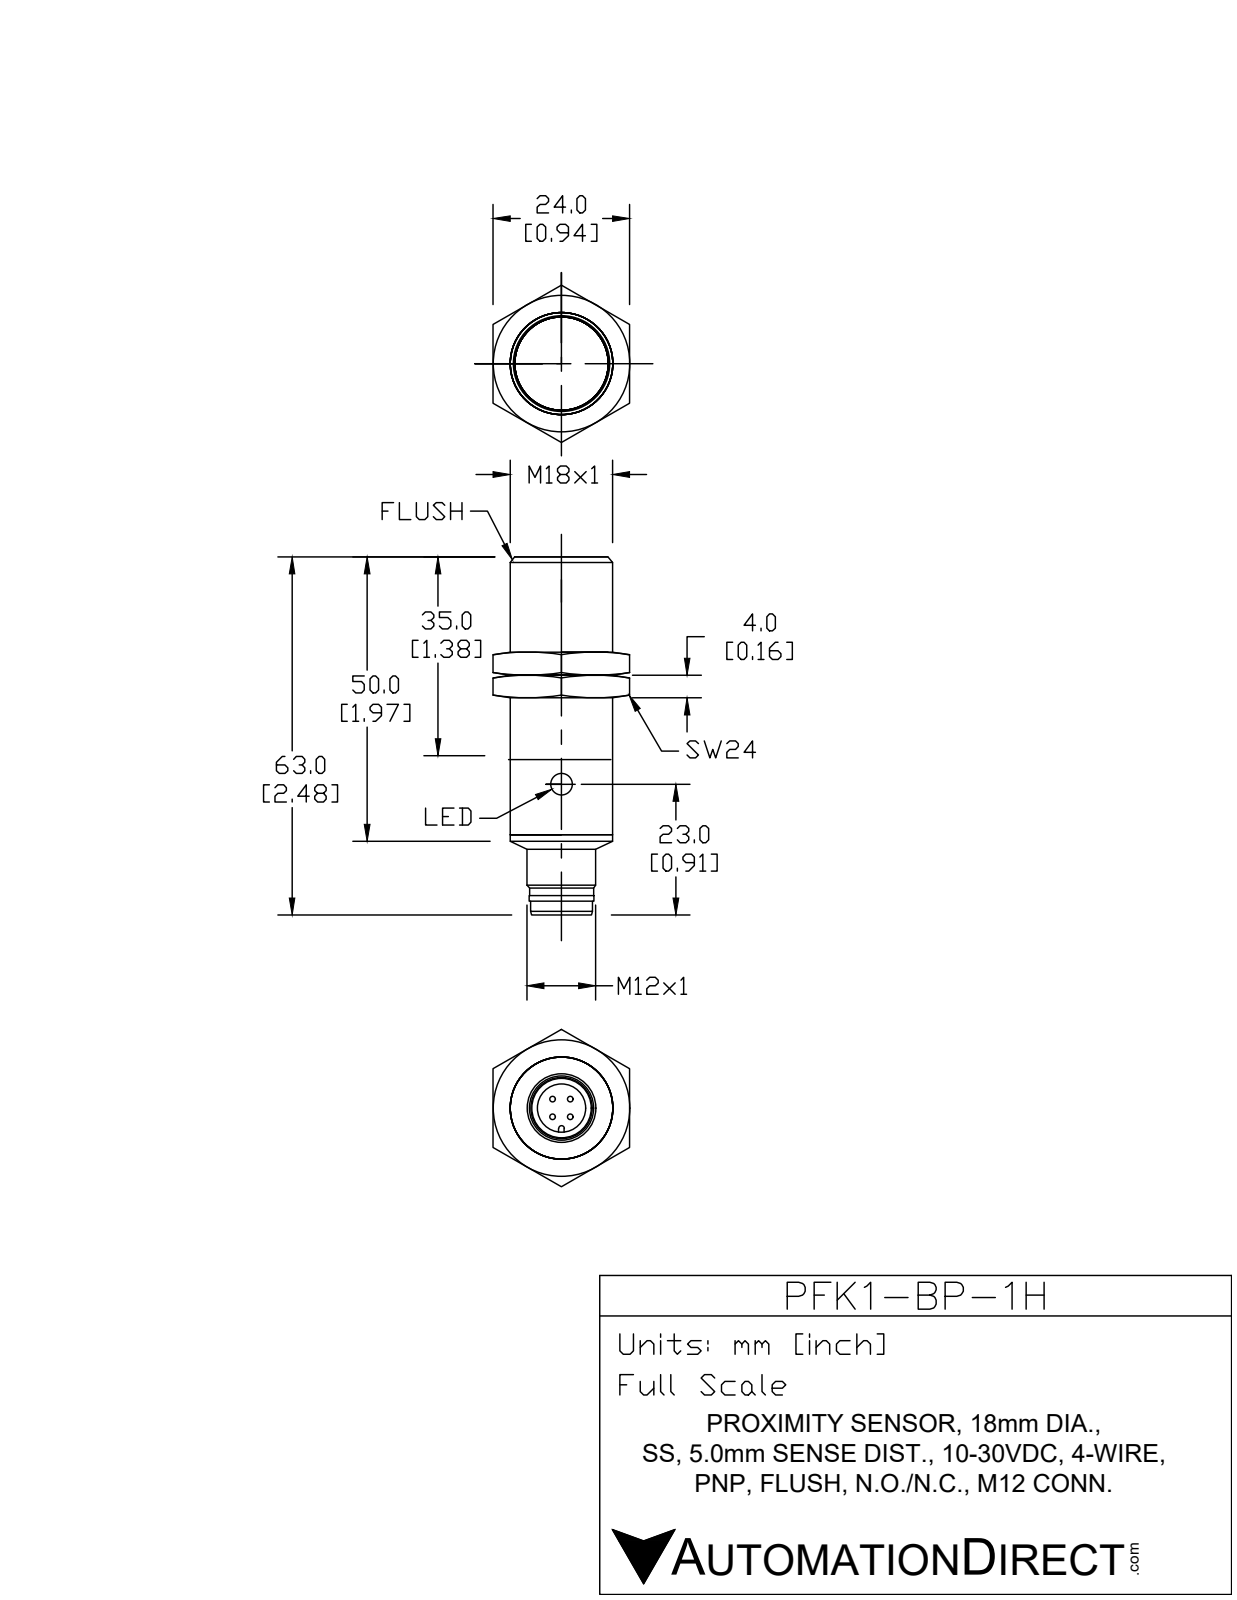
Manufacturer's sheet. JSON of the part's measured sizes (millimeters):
{"part_name": "PFK1-BP-1H", "step_written_by": "SolidWorks 2017 (AUTOMOTIVE_DESIGN)", "units": "millimeters", "bodies": {"solids": 4, "faces": 69, "planar": 12, "cylindrical": 35, "other": 22}, "overall_size": [63.1, 18, 18], "volume_mm3": 13700, "surface_area_mm2": 6632, "round_holes": [[4, 1], [8.4, 1], [8.5, 1], [9.5, 1], [15.8, 1]], "round_bosses_or_shafts": [[1, 4], [18, 1], [12, 1], [10.5, 1], [9.4, 1]], "partial_cylinders_radius": [[0.6, 1], [8.3, 1]], "face_to_face_distances": [39.1, 10, 49.1, 53, 43, 3.9, 54.2, 44.2, 5.1, 1.2]}
